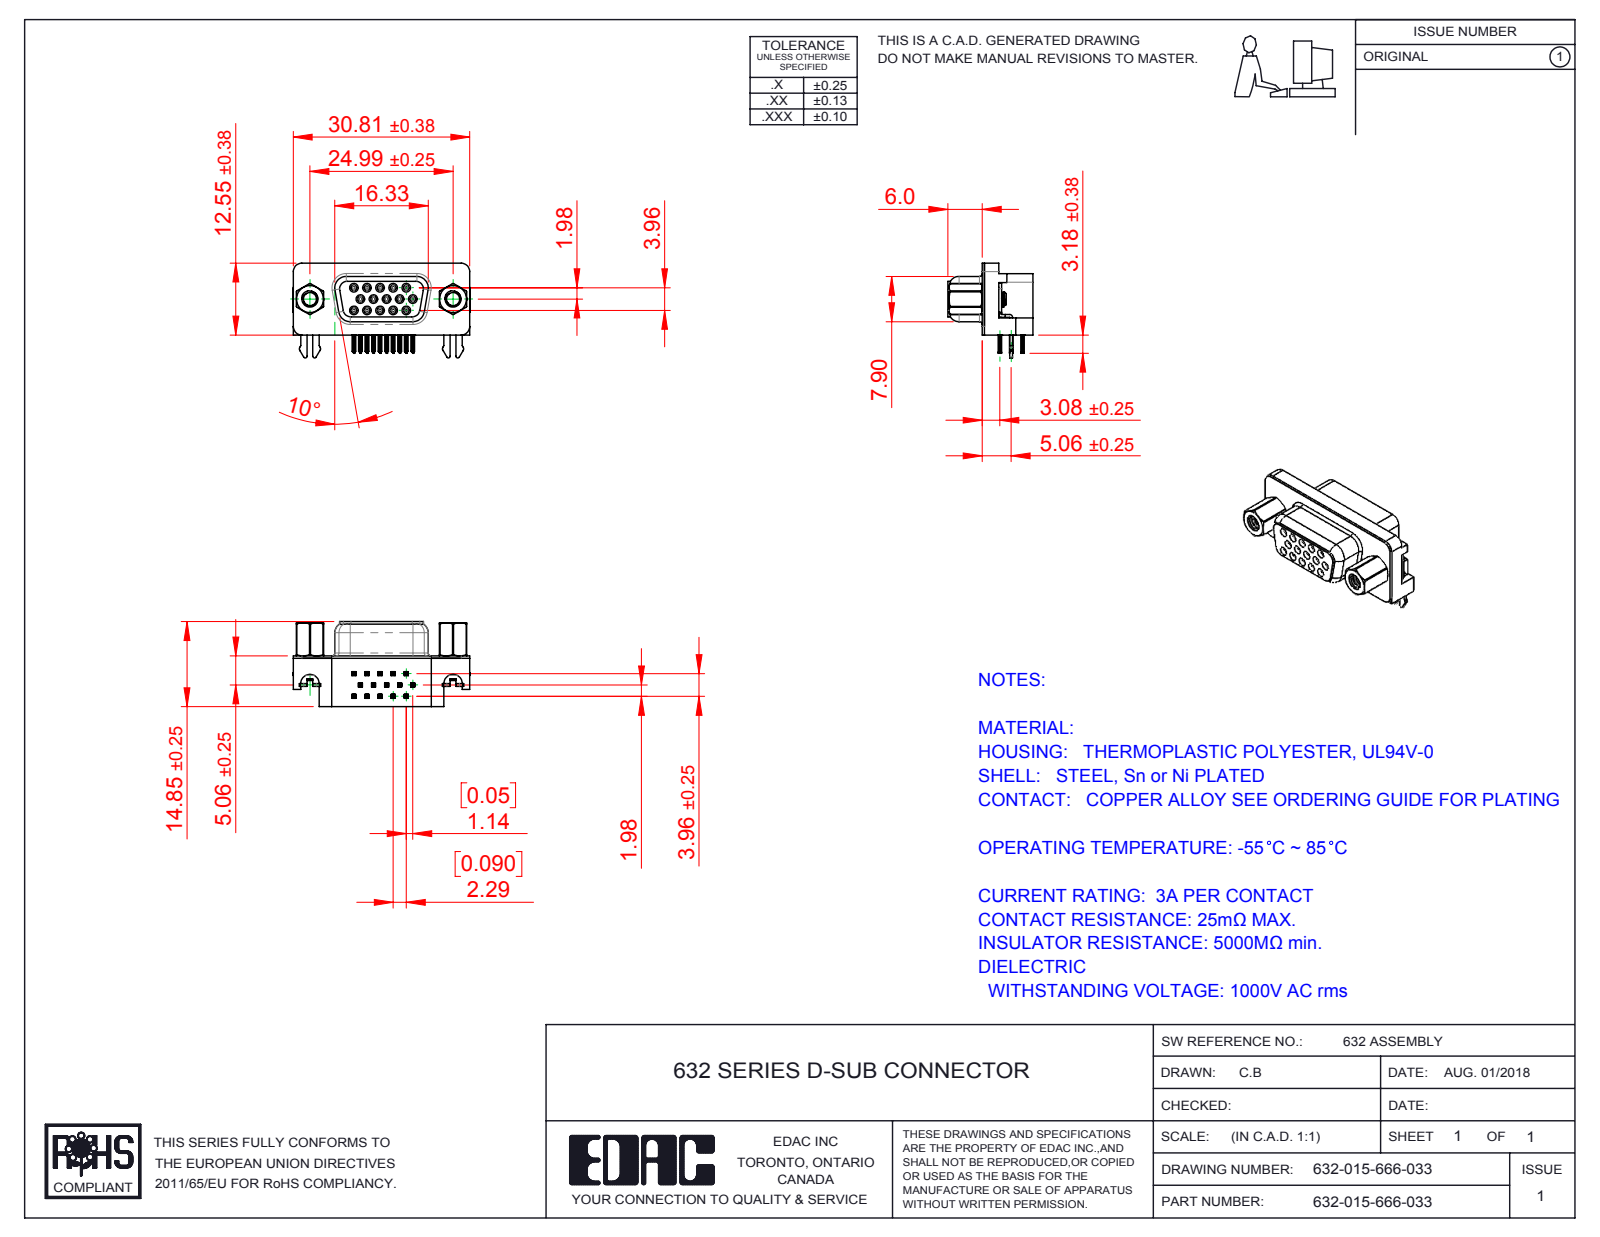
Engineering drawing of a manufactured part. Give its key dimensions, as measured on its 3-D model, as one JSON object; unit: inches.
{"part_name": "632-015-666-003; 632 4-40 Hex Standoff 5; 632 Housing_15 Socket; 632 Shell_9 Socket (+4 more)", "step_written_by": "SolidWorks 2016 (CONFIG_CONTROL_DESIGN)", "units": "inches", "bodies": {"solids": 21, "faces": 2376, "planar": 996, "cylindrical": 646, "other": 734}, "overall_size": [1.216, 0.652, 0.585], "volume_in3": 0.186, "surface_area_in2": 8.029, "round_holes": [[0.031, 15], [0.035, 15], [0.09, 2], [0.157, 2], [0.189, 2], [0.197, 2]], "round_bosses_or_shafts": [[0.047, 15], [0.193, 2], [0.11, 2]], "partial_cylinders_radius": [[0.004, 120], [0.006, 60], [0.014, 30], [0.013, 15], [0.039, 11], [0.011, 10], [0.02, 10], [0.053, 8]], "face_to_face_distances": [0.016, 0.078, 0.333, 0.348, 0.114, 0.098, 0.234, 0.264, 0.278, 0.125], "hole_center_spacings": [0.09, 0.09, 0.156, 0.18, 0.238, 0.156, 0.18, 0.27]}
